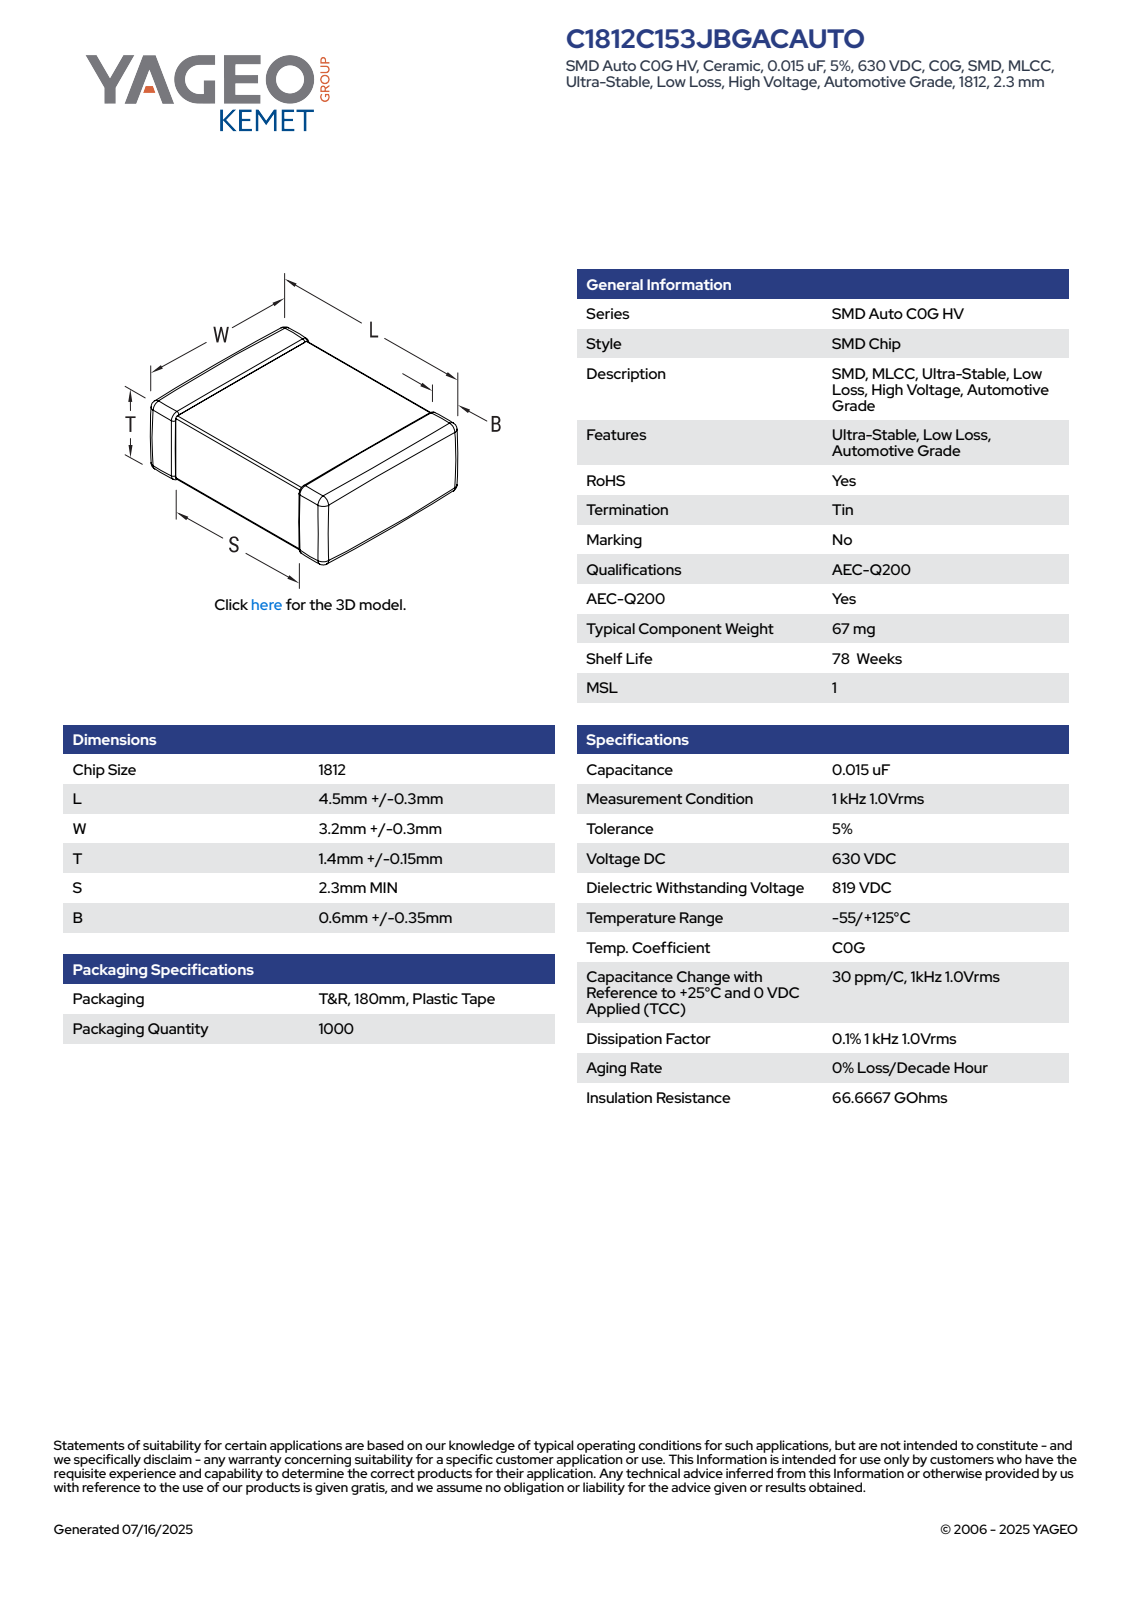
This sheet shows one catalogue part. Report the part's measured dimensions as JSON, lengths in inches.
{"part_name": "CCS_CCSTD_1812_L4.8W3.5T1.55B0.6", "step_written_by": "SolidWorks 2021 (AUTOMOTIVE_DESIGN)", "units": "inches", "bodies": {"solids": 4, "faces": 129, "planar": 71, "cylindrical": 42, "other": 16}, "overall_size": [0.189, 0.138, 0.061], "volume_in3": 0.001, "surface_area_in2": 0.091, "face_to_face_distances": [0.058, 0.056, 0.061, 0.189, 0.135, 0.132, 0.138, 0.082, 0.107, 0.102]}
